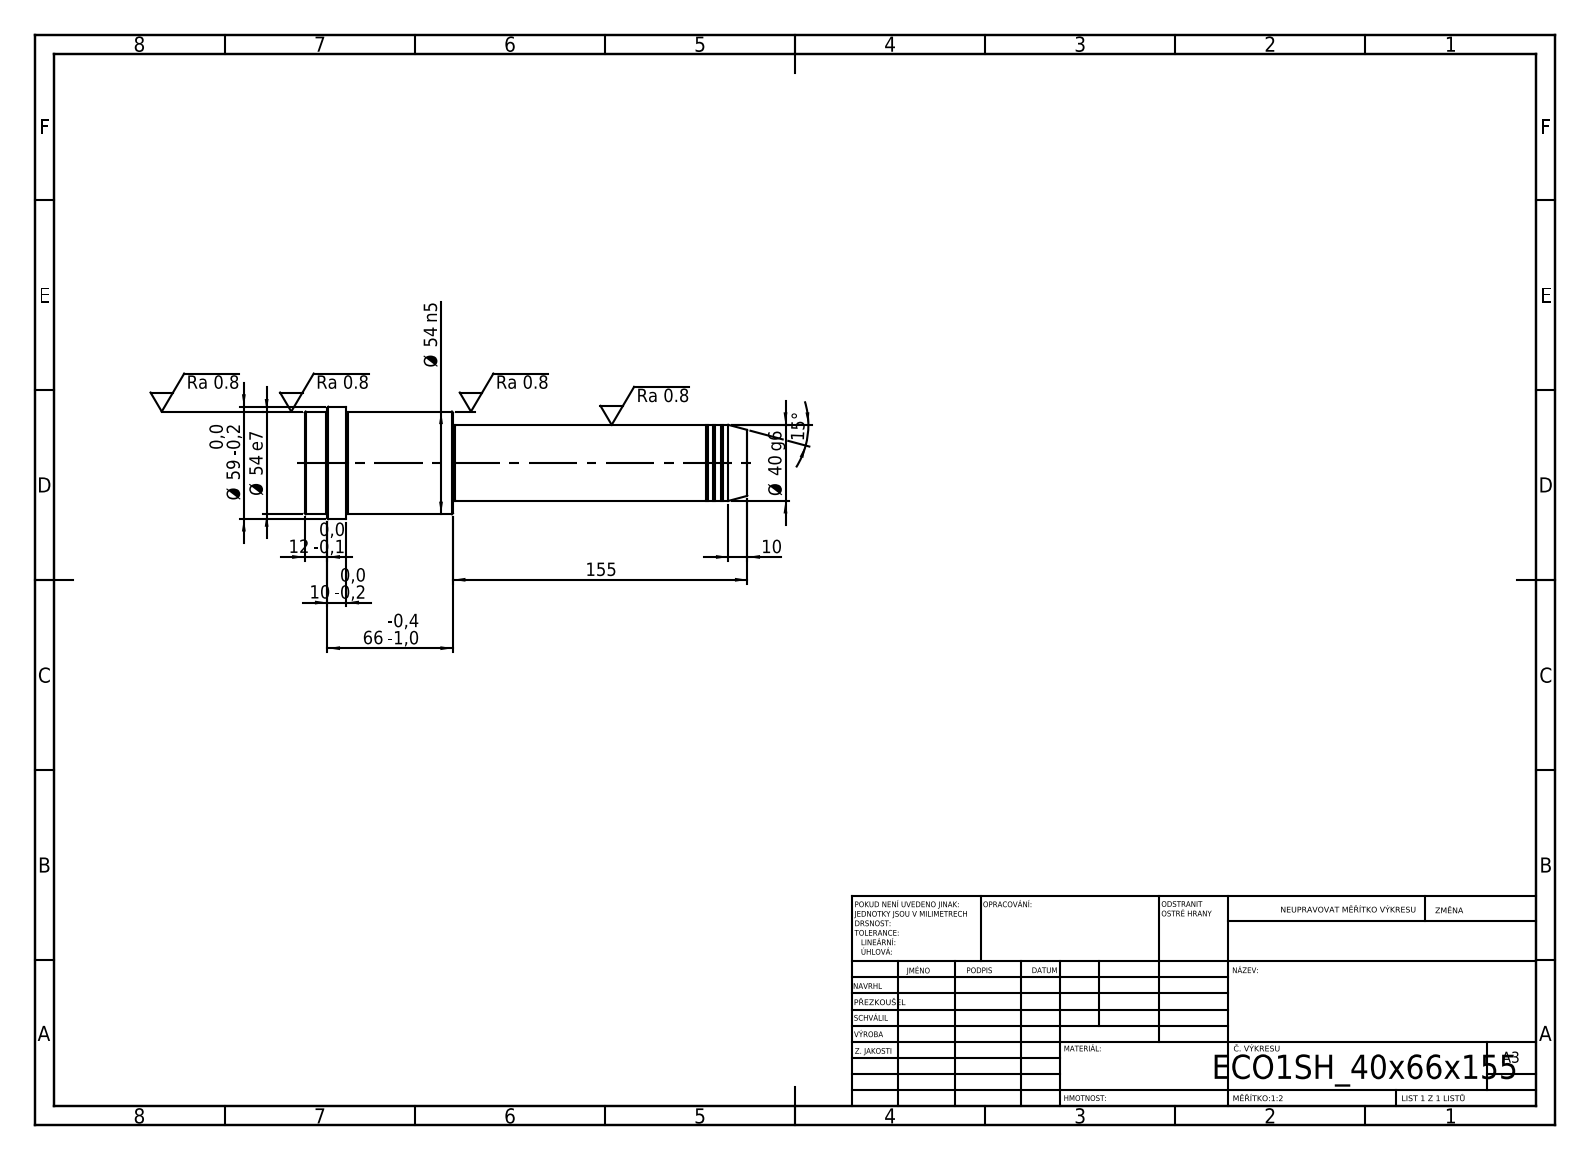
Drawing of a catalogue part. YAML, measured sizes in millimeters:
step_written_by: "SolidWorks 2019 (CONFIG_CONTROL_DESIGN)"
units: millimeters
bodies: {solids: 1, faces: 52, planar: 6, cylindrical: 16, other: 30}
overall_size: [233, 59, 59]
volume: 375836
surface_area: 38325
round_bosses_or_shafts:
  - {diameter: 59, count: 1}
  - {diameter: 54, count: 1}
  - {diameter: 40, count: 1}
  - {diameter: 39, count: 1}
face_to_face_distances: [78, 155, 233, 211, 56, 22, 221, 66, 10, 12]
